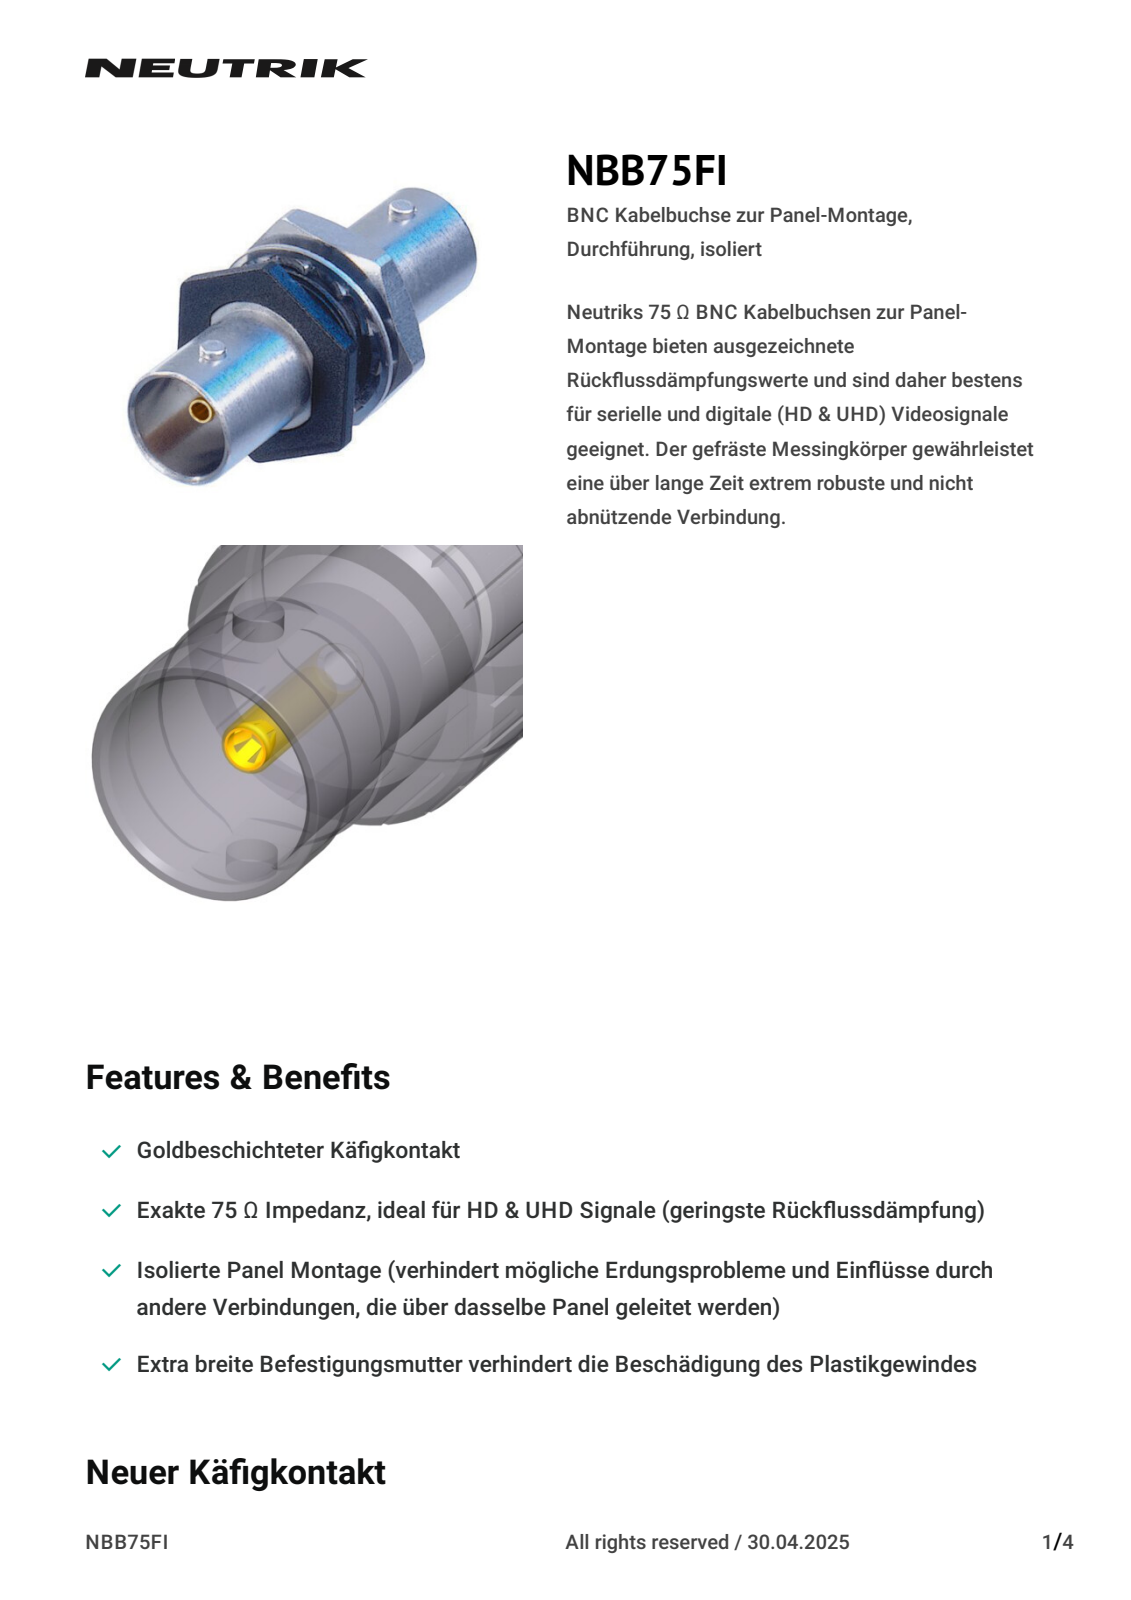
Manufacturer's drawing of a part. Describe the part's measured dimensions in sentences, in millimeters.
The part is named "NBB75FI". Its 3-D file was written by "CREO PARAMETRIC BY PTC INC, 2019080 (CONFIG_CONTROL_DESIGN)". It is 1 solid with 147 faces: 39 planar, 66 cylindrical and 42 other. Overall it measures 34 by 11.1 by 9.7 millimeters. Its volume is 1 722 cubic millimeters and its surface area 1 782 square millimeters. Round holes: 1 of diameter 1.75. Round bosses or shafts: 2 of diameter 1.95, 1 of diameter 9.7, 1 of diameter 9.62, 1 of diameter 2.2, 1 of diameter 2.12. Partial cylindrical surfaces (rounded edges, fillets, slot ends): 4 of radius 1.4, 2 of radius 2.75, 1 of radius 4.66, 1 of radius 5.25, 1 of radius 5.5, 1 of radius 5.55. The main face-to-face distances are 18, 9.7, 3, 15, 9.22, 9.8, 9.32, 12.8, 5.2, 8.
